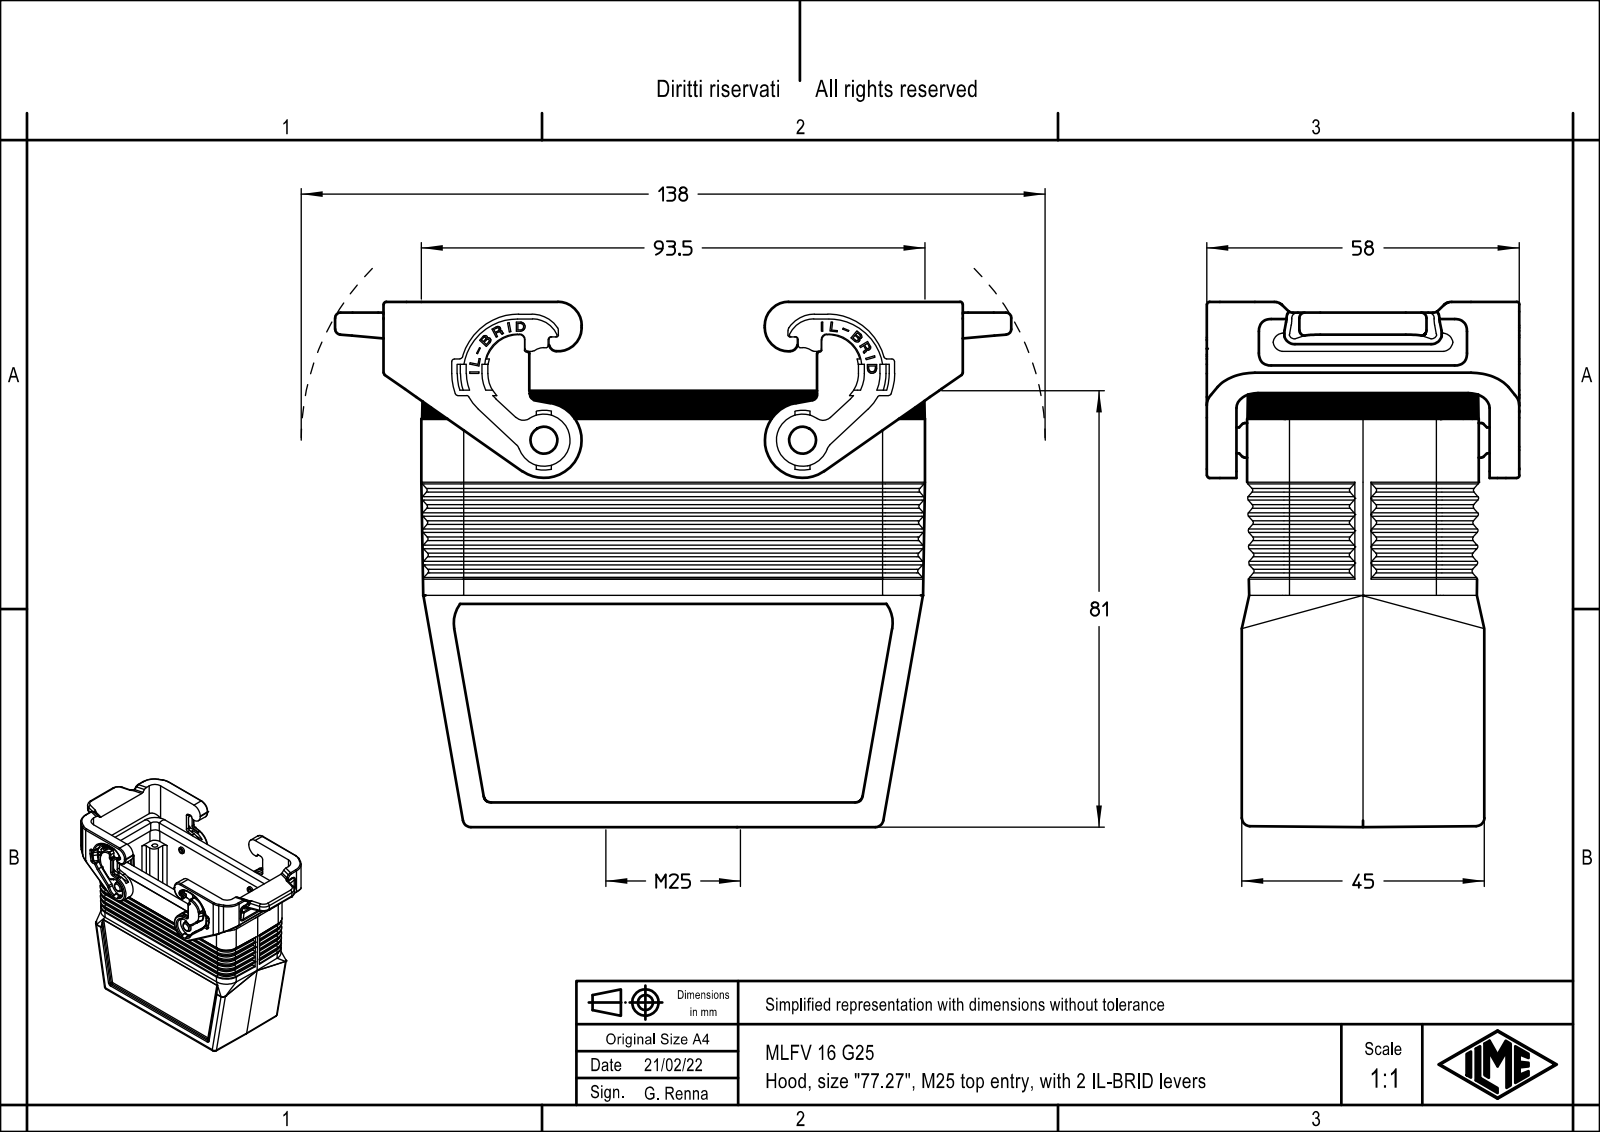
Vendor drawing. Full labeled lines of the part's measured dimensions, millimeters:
Part name (STEP PRODUCT): MLFV_16_G25
STEP written by: Creo Elements/Direct Modeling 20.1B 02-Apr-2019 (C) Parametric Technology GmbH (AUTOMOTIVE_DESIGN)
Units: millimetres
Bodies: 1 solid, 1598 faces (1028 planar, 391 cylindrical, 179 other)
Overall size (bounding box): 125.5 × 97.45 × 58
Volume: 120 585 mm³ · Surface area: 61 391 mm²
Round holes (diameter × count): ⌀2.75 ×4, ⌀23.6 ×1
Round bosses / shafts (diameter × count): ⌀6.8 ×2, ⌀4.8 ×2
Partial cylindrical surfaces — rounded edges, fillets, slot ends (radius × count): R0.5 ×104, R1 ×46, R3 ×20, R7 ×16, R0.33 ×15, R1.5 ×14, R0.3 ×8, R2 ×8
Main face-to-face distances: 39.25, 3.75, 2, 1, 5.75, 4.75, 43, 45, 34.5, 38.25
Hole centre spacings: 41.03, 27, 77.5, 82.07
